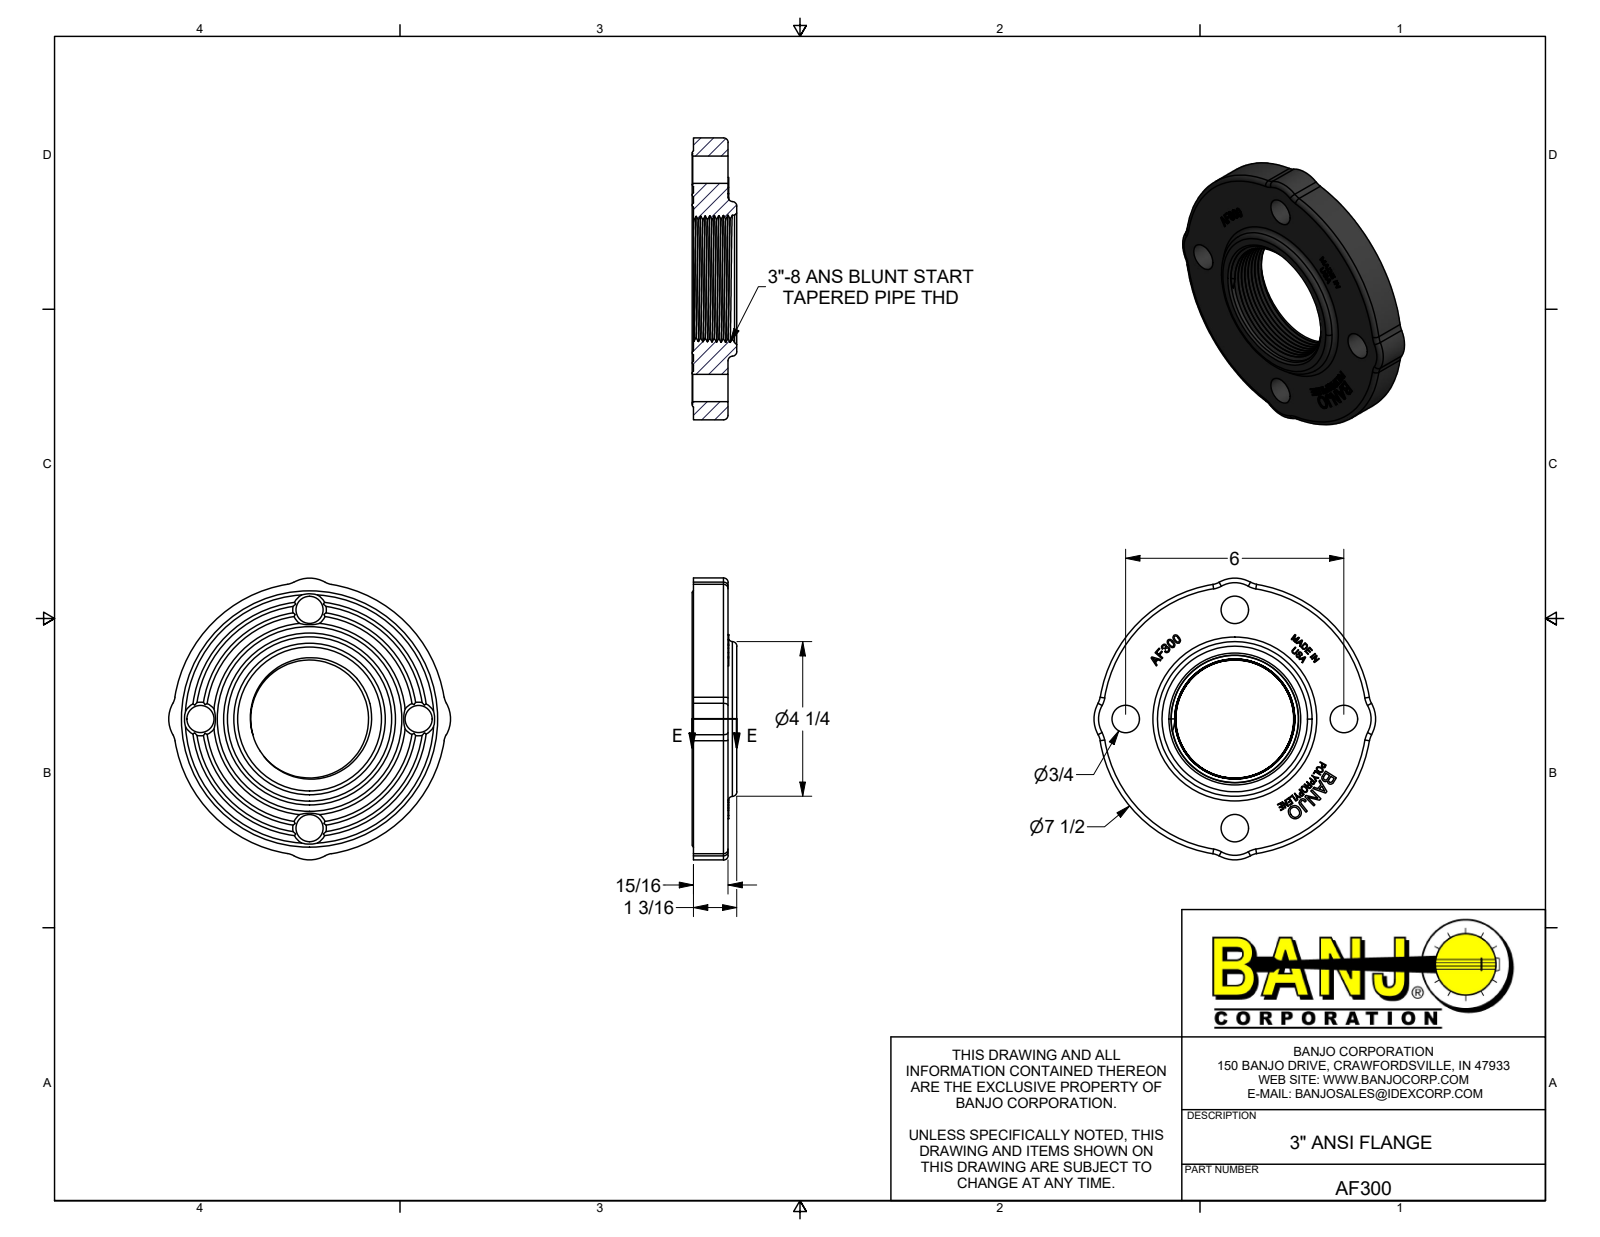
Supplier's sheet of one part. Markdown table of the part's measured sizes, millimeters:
| quantity | value |
| --- | --- |
| part name | AF300 |
| STEP written by | Autodesk Inventor 2014 (AUTOMOTIVE_DESIGN) |
| units | millimeters |
| bodies | 1 solid, 511 faces (301 planar, 21 cylindrical, 189 other) |
| overall size | 196.85 × 196.85 × 31.11 |
| volume | 549 255 mm³ |
| surface area | 80 727 mm² |
| round holes (diameter × count) | 19.05 × 4 |
| round bosses / shafts (diameter × count) | 190.5 × 1 |
| partial cylindrical surfaces (radius × count) | 12.7 × 8, 22.23 × 4, 24.69 × 1 |
| main face-to-face distances | 24.13, 30.23, 6.1, 24.64, 0.51, 5.59, 0.55, 0.46, 0.54, 1.15 |
| hole center spacings | 107.76, 152.4 |
